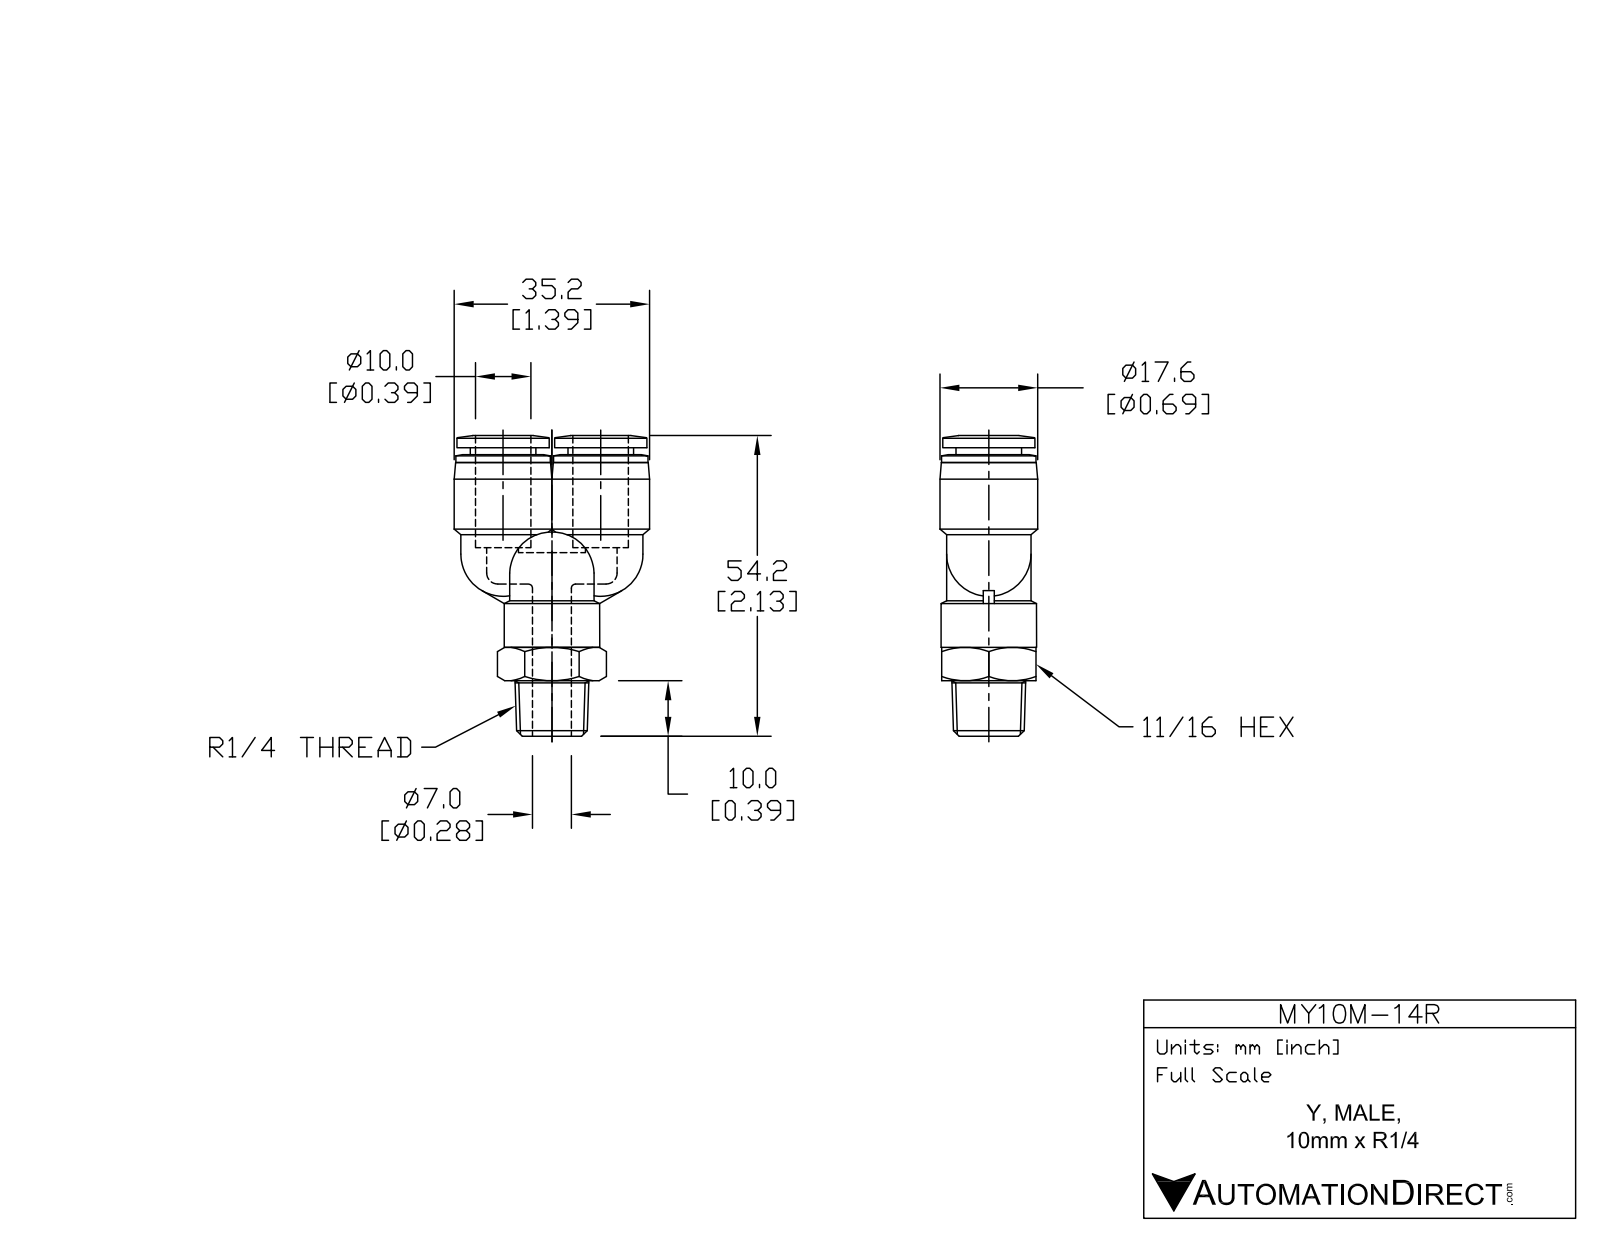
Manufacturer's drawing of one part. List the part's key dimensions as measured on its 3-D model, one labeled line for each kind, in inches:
Part name (STEP PRODUCT): MY10M-14R
STEP written by: SolidWorks 2015 (AUTOMOTIVE_DESIGN)
Units: inches
Bodies: 1 solid, 110 faces (24 planar, 35 cylindrical, 51 other)
Overall size (bounding box): 2.136 × 1.386 × 0.693
Volume: 0.678 in³ · Surface area: 11.79 in²
Round holes (diameter × count): ⌀0.315 ×4, ⌀0.406 ×2
Round bosses / shafts (diameter × count): ⌀0.598 ×3, ⌀0.693 ×2, ⌀0.669 ×2, ⌀0.654 ×2, ⌀0.465 ×2, ⌀0.677 ×1
Main face-to-face distances: 0.669, 0.049, 1.606, 1.656, 0.943, 0.663, 0.713, 0.394, 1.337, 2
Hole centre spacings: 0.346, 0.693
